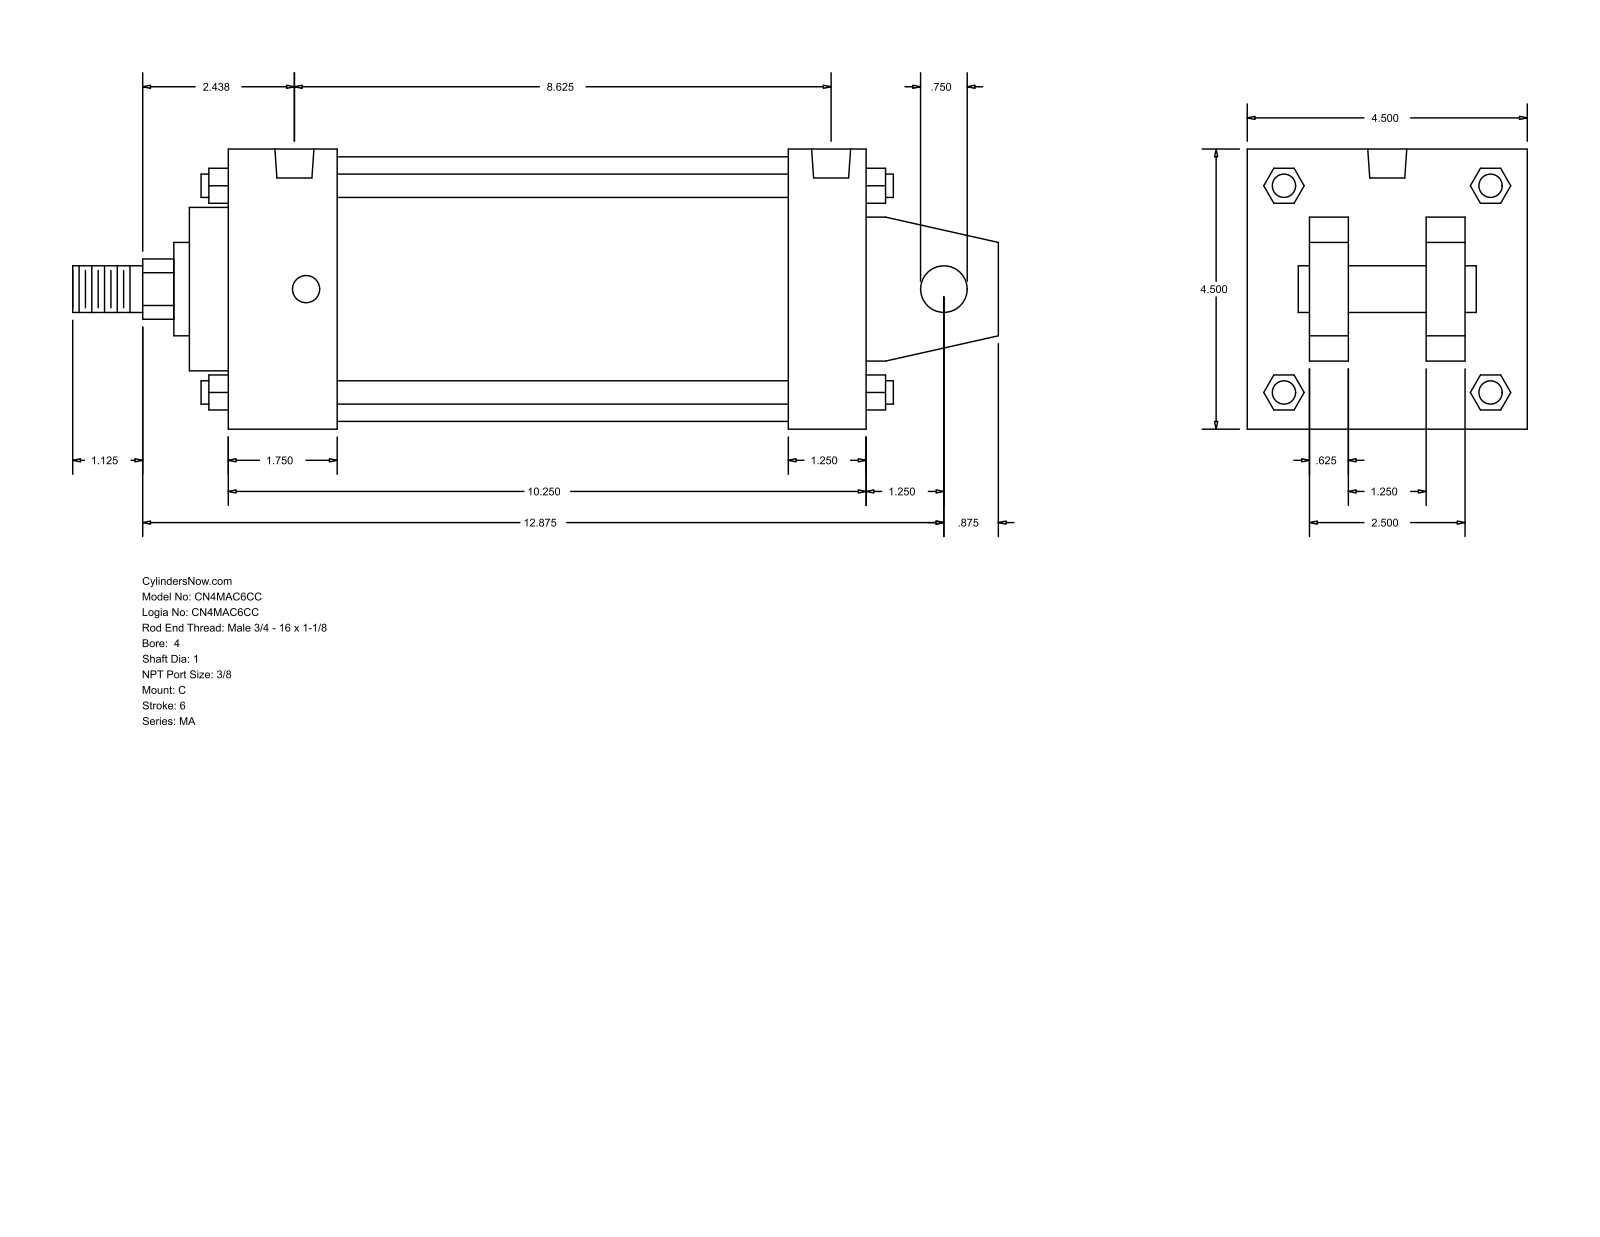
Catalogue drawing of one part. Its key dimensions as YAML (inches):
part_name: "MA_C__0400_1"
step_written_by: "GSSL Pune (CONFIG_CONTROL_DESIGN)"
units: inches
bodies: {solids: 0, faces: 141, planar: 109, cylindrical: 32, other: 0}
overall_size: [14.875, 4.5, 4.5]
round_holes:
  - {diameter: 0.437, count: 4}
  - {diameter: 0.627, count: 2}
round_bosses_or_shafts:
  - {diameter: 0.375, count: 4}
  - {diameter: 0.75, count: 2}
  - {diameter: 4.25, count: 1}
  - {diameter: 2.625, count: 1}
  - {diameter: 1.5, count: 1}
  - {diameter: 1, count: 1}
partial_cylinders:
  - {radius: 0.484, count: 1}
face_to_face_distances: [4.5, 10.25, 0.625, 2.875, 1.625, 1, 3.5, 1.875, 9, 1.25]
hole_center_spacings: [0.187, 8.25, 8.438, 8.625]
